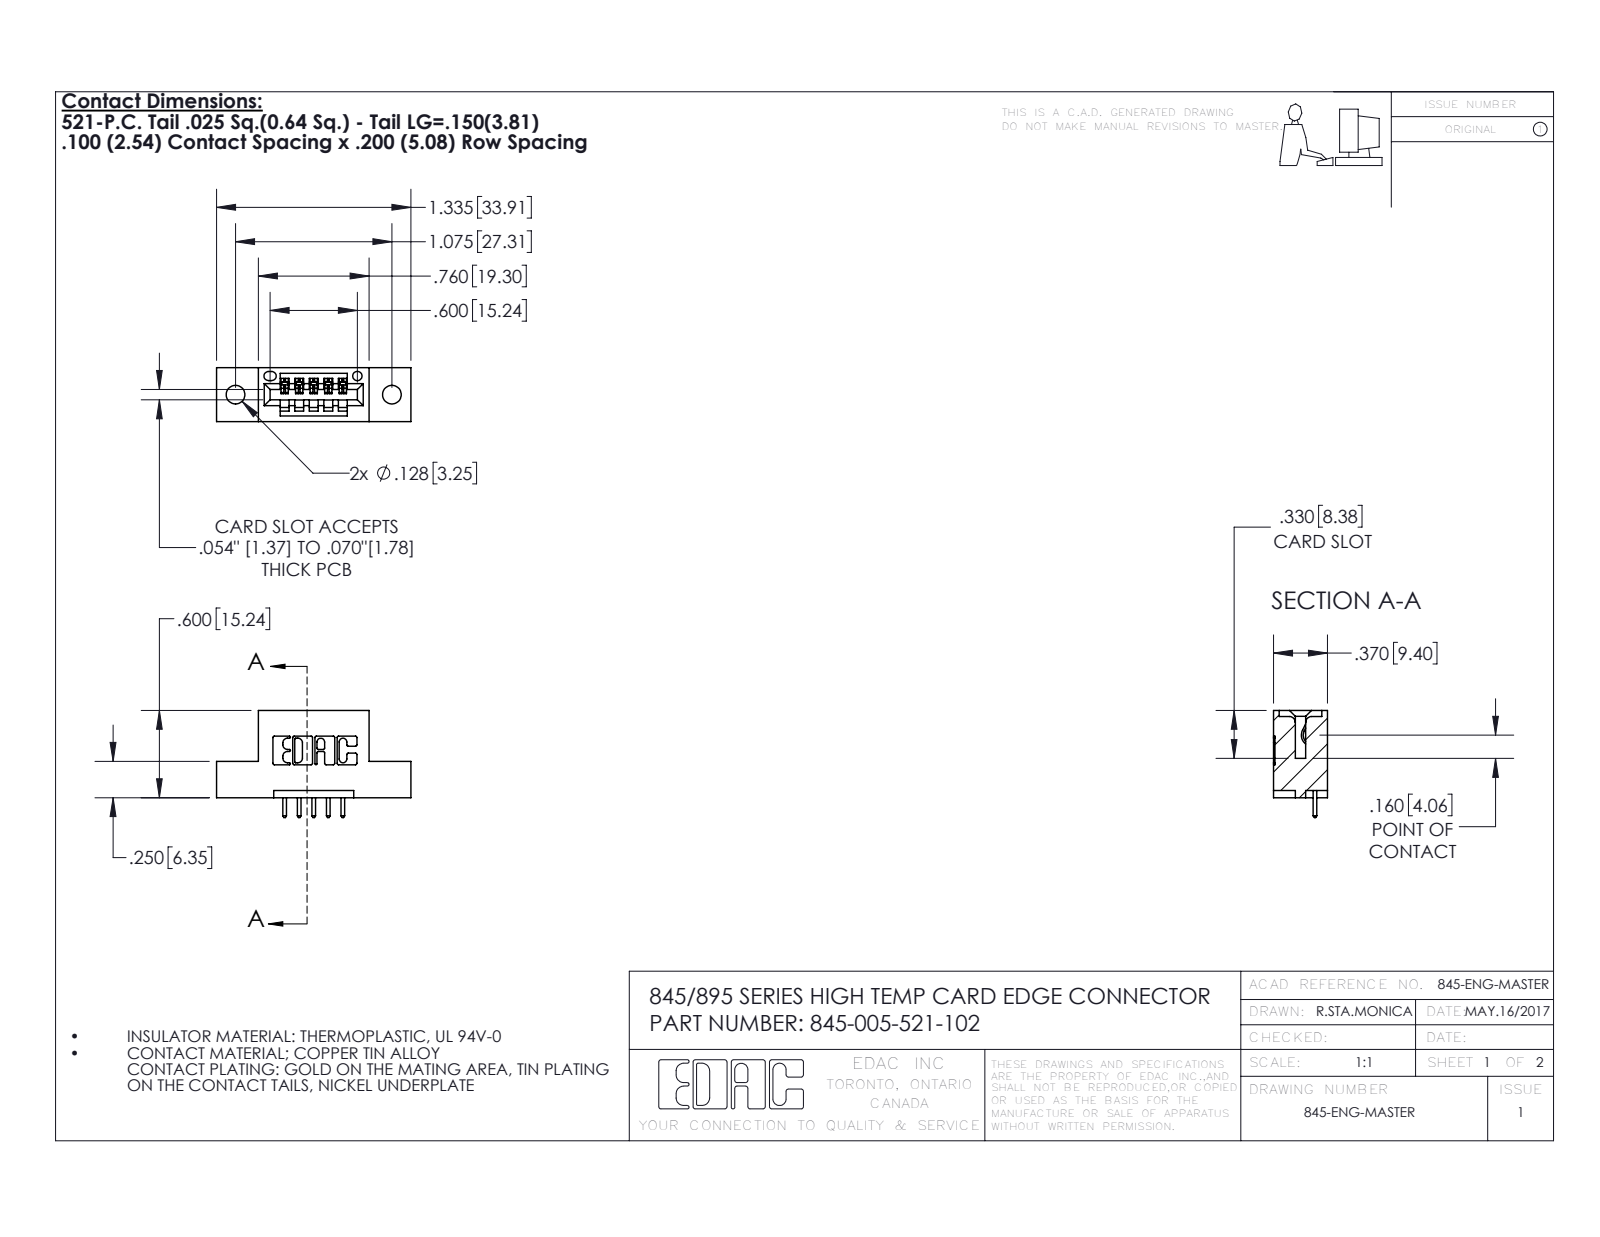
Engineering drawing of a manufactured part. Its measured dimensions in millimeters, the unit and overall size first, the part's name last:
Units: millimetres
Overall size (bounding box): 33.9 × 18.7 × 9.4
Round holes (diameter × count): ⌀3.3 ×2, ⌀1.6 ×1
Partial cylindrical surfaces — rounded edges, fillets, slot ends (radius × count): R0.3 ×22, R0.2 ×10, R0.3 ×10, R0.2 ×6, R0.8 ×6, R0.7 ×3, R0.8 ×2, R1 ×2
Main face-to-face distances: 5.1, 9.4, 7.6, 1.8, 2.5, 6.4, 0.6, 2.5, 6.9, 1.5
Hole centre spacings: 6.9, 21.5, 27.3
Volume: 2 870 mm³ · Surface area: 2 979 mm²
Bodies: 6 solids, 416 faces (280 planar, 136 cylindrical, 0 other)
Part name (STEP PRODUCT): 345-292-001_345-293-121; 345 Part_Flush Mounting Lugs - 0.128 Dia; 345-005-521-102
STEP written by: SolidWorks 2016 (CONFIG_CONTROL_DESIGN)
